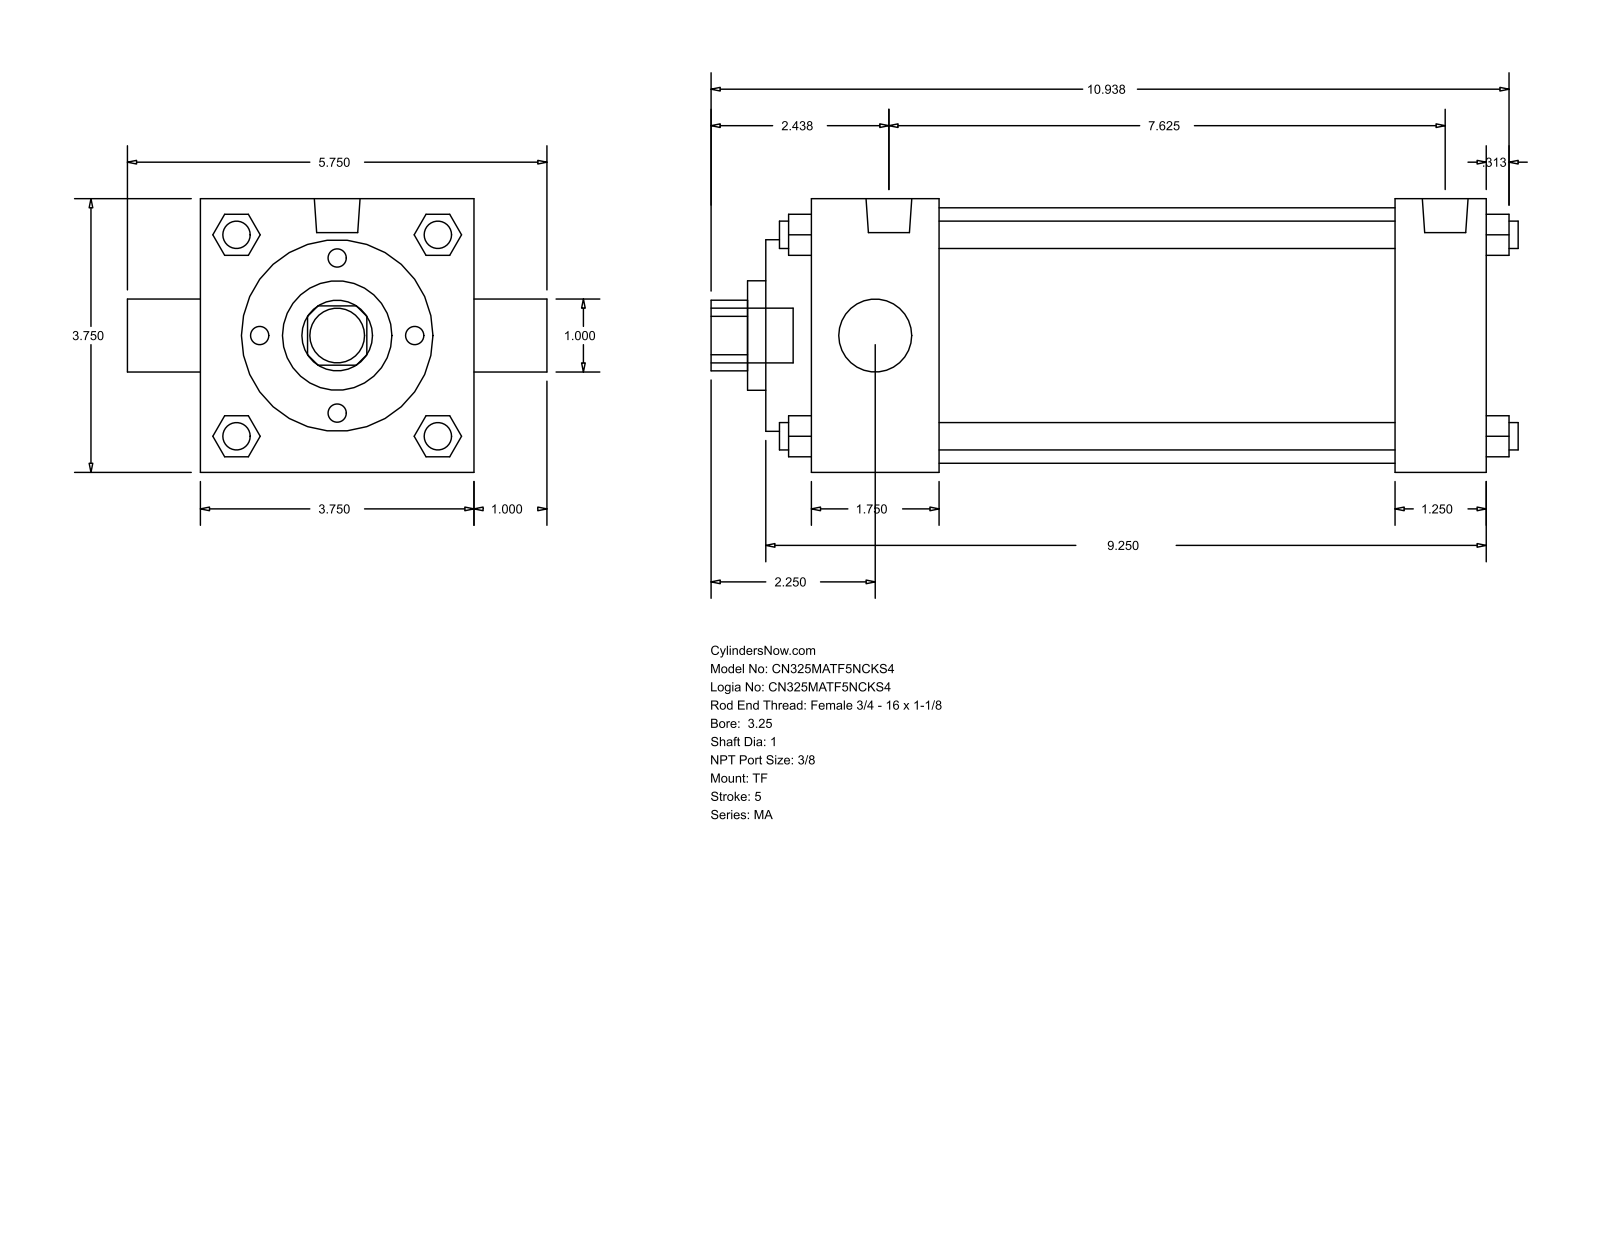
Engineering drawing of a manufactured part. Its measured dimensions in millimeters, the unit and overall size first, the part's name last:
Units: millimetres
Overall size (bounding box): 280.99 × 146.05 × 95.25
Round holes (diameter × count): ⌀25.4 ×2, ⌀38.1 ×1, ⌀66.67 ×1, ⌀88.9 ×1
Round bosses / shafts (diameter × count): ⌀9.53 ×4, ⌀11.11 ×3, ⌀15.93 ×2, ⌀19.05 ×1
Partial cylindrical surfaces — rounded edges, fillets, slot ends (radius × count): R12.29 ×1
Main face-to-face distances: 95.24, 234.96, 15.87, 44.46, 203.2, 158.74, 190.5, 31.76, 60.33, 219.07
Bodies: 0 solids, 122 faces (93 planar, 29 cylindrical, 0 other)
Part name (STEP PRODUCT): MA_TF__0325_1
STEP written by: GSSL Pune (CONFIG_CONTROL_DESIGN)
